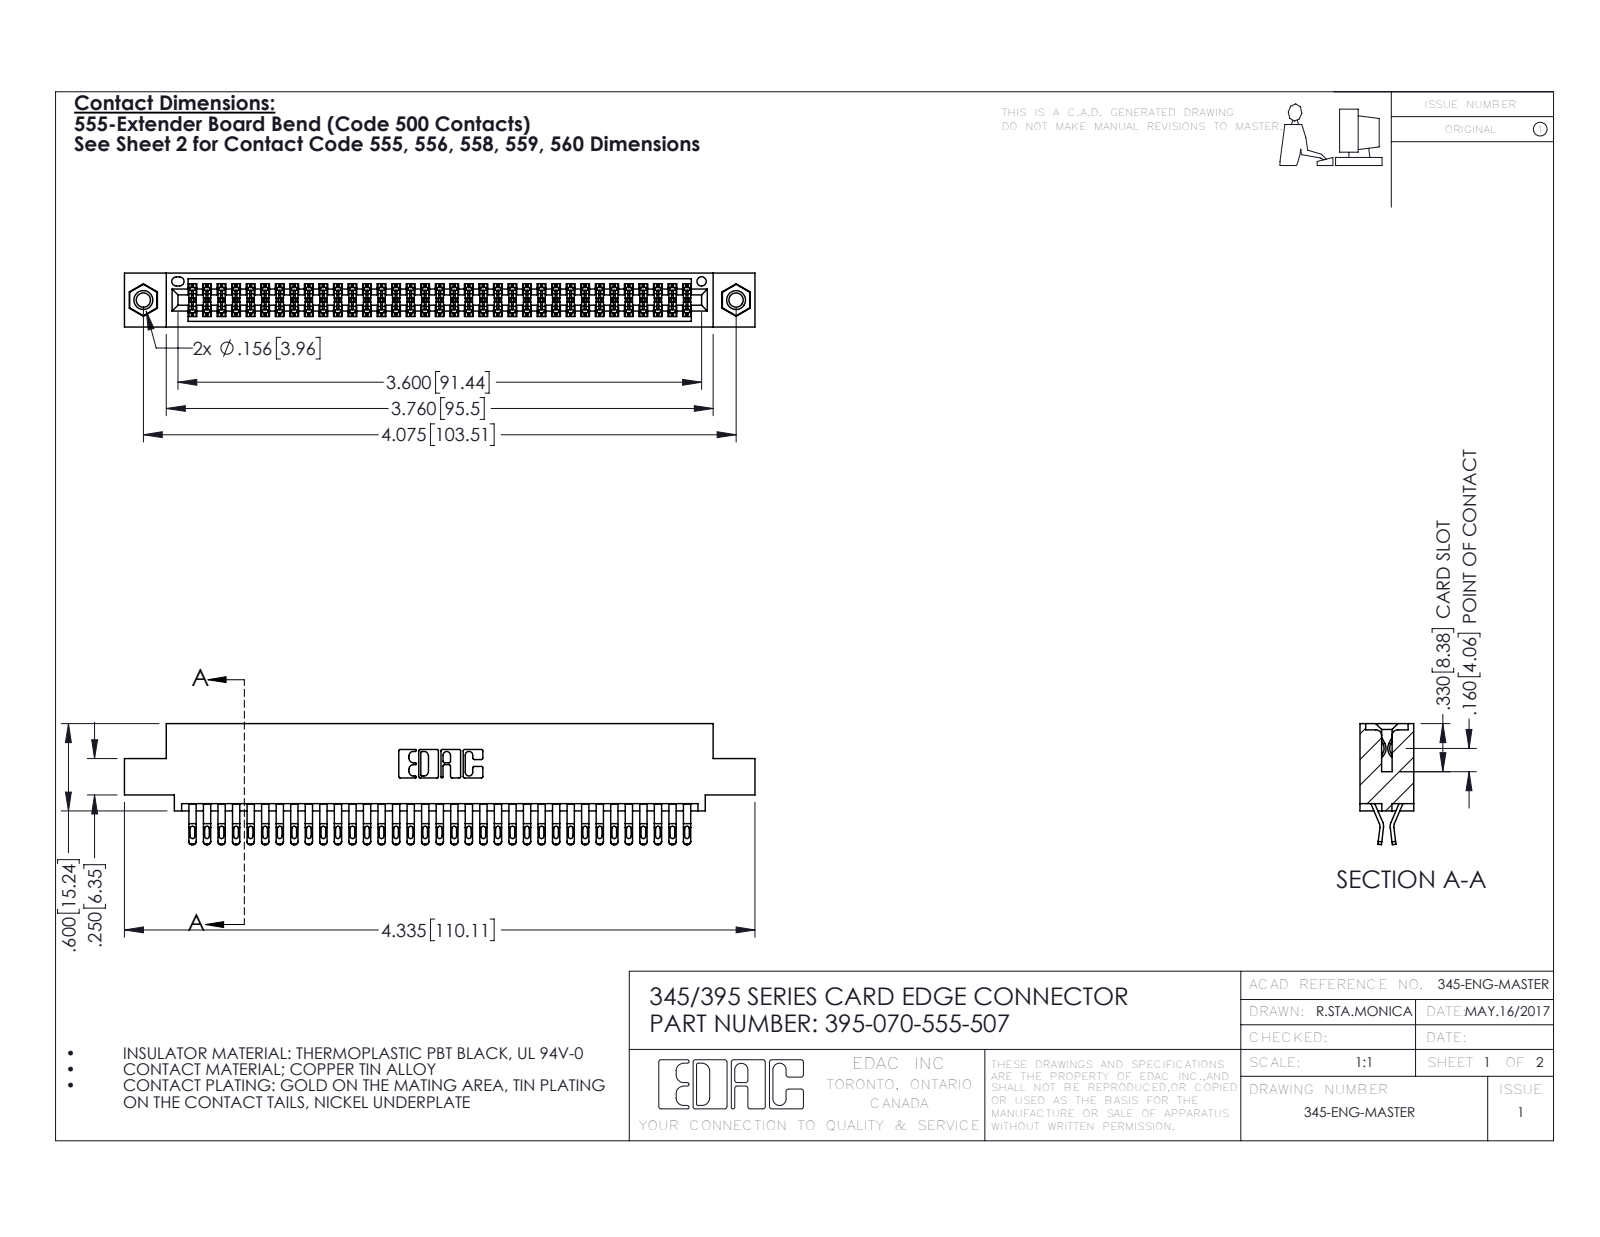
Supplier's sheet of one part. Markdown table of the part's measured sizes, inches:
| quantity | value |
| --- | --- |
| part name | 345-292-001_555 Tail; 345-250-001_345-250-005-103; 395-070-555-507; 345 Part_0.110 Offset - 0.156 Dia-TI |
| STEP written by | SolidWorks 2016 (CONFIG_CONTROL_DESIGN) |
| units | inches |
| bodies | 73 solids, 4110 faces (2286 planar, 1808 cylindrical, 16 other) |
| overall size | 4.335 × 0.832 × 0.37 |
| volume | 0.656 in³ |
| surface area | 25.7 in² |
| round holes (diameter × count) | 0.098 × 2, 0.125 × 2, 0.156 × 2, 0.064 × 1 |
| round bosses / shafts (diameter × count) | 0.155 × 2 |
| partial cylindrical surfaces (radius × count) | 0.016 × 175, 0.02 × 140, 0.006 × 105, 0.01 × 22, 0.007 × 6, 0.031 × 6, 0.026 × 3, 0.01 × 2 |
| main face-to-face distances | 0.072, 0.298, 0.37, 0.025, 0.2, 0.098, 0.272, 0.225, 0.175, 0.149 |
| hole center spacings | 0.27, 3.839, 4.075 |
